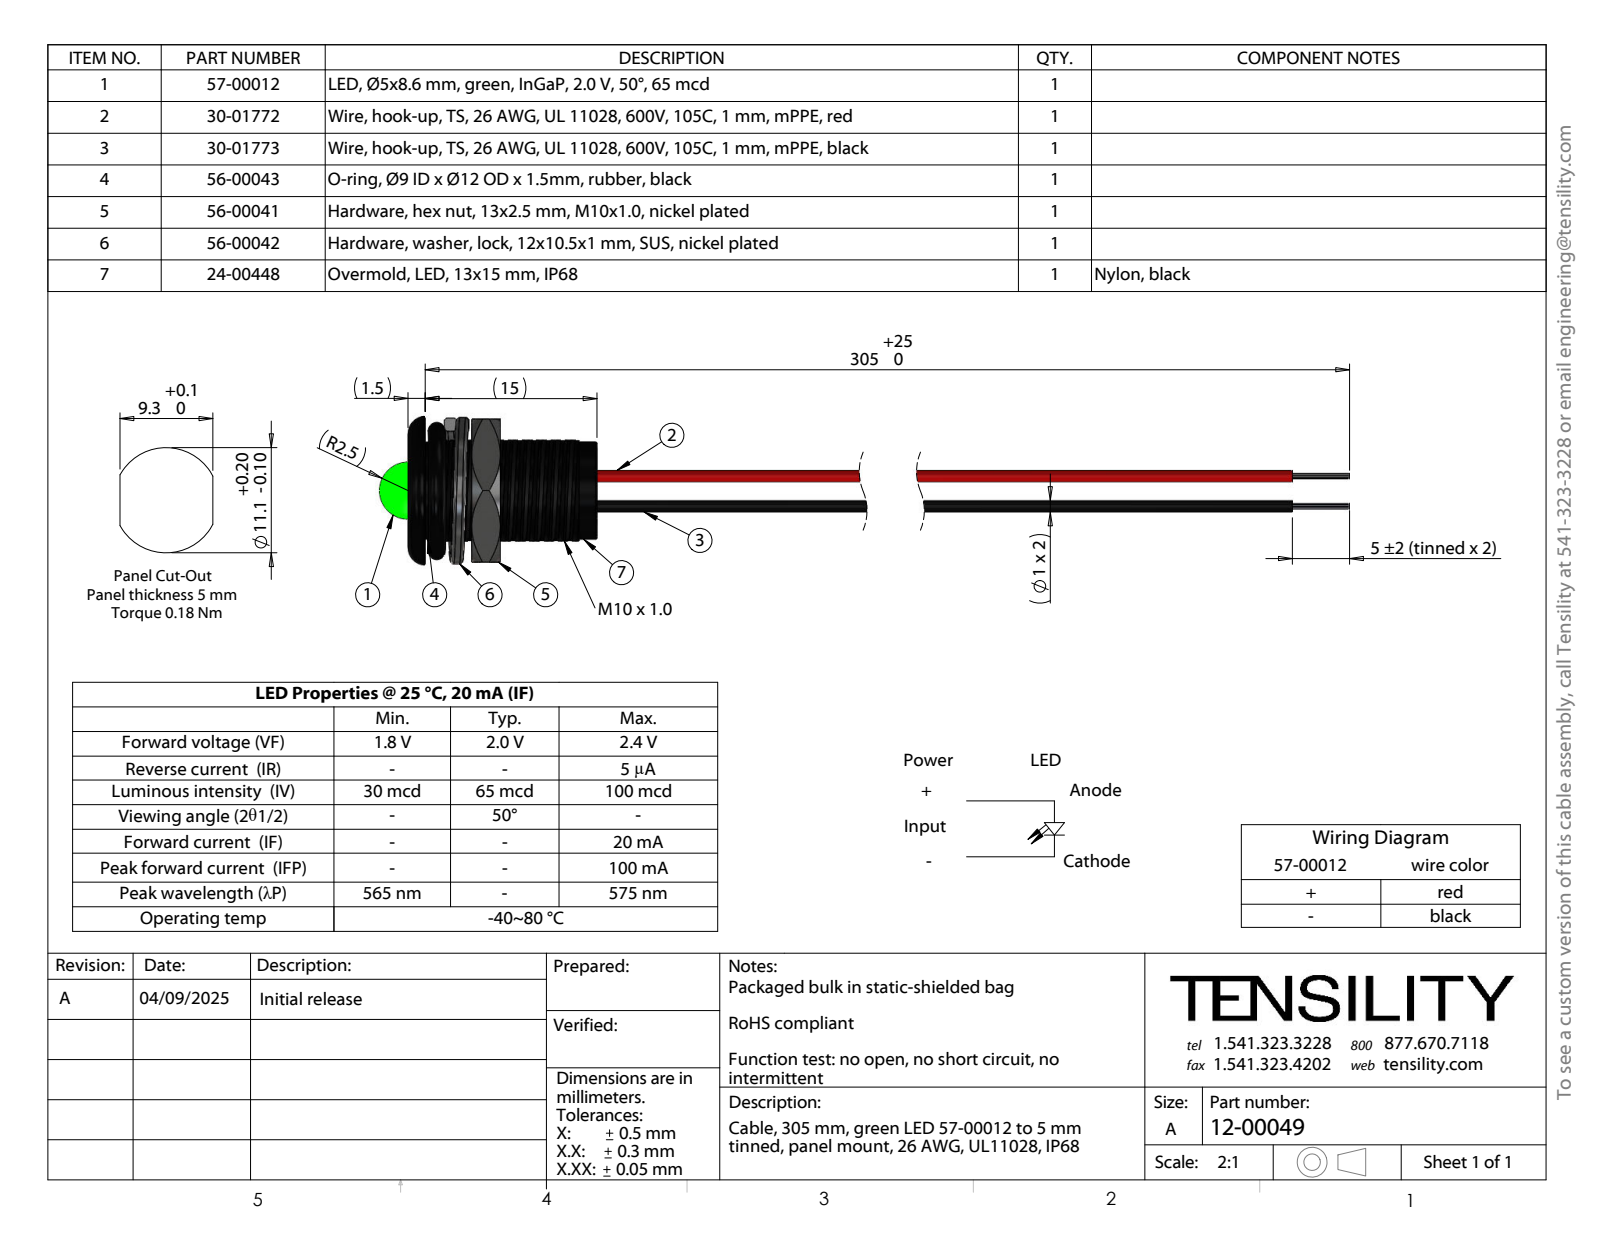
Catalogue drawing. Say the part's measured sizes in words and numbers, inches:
The part is named "57-00012_trimmed leads; 56-00042_Split washer; 30-01772_stripped and tinned; 30-01773_stripped and tinned (+4 more)". Its 3-D file was written by "SolidWorks 2021 (CONFIG_CONTROL_DESIGN)". It is 57 solids with 514 faces: 185 planar, 246 cylindrical and 83 other. Overall it measures 6.85 by 0.568 by 0.511 inches. Its volume is 0.108 cubic inches and its surface area 10.18 square inches. Round holes: 2 of diameter 0.039. Round bosses or shafts: 2 of diameter 0.039, 2 of diameter 0.033, 1 of diameter 0.335, 1 of diameter 0.197. Partial cylindrical surfaces (rounded edges, fillets, slot ends): 1 of radius 0.17, 1 of radius 0.197. The main face-to-face distances are 0.059, 0.65, 0.591, 0.492, 0.317, 0.258, 0.332, 0.219, 0.16, 0.098. The hole center spacings are 0.014, 0.015, 0.013, 0.096, 0.093, 0.098, 0.099, 0.101.
